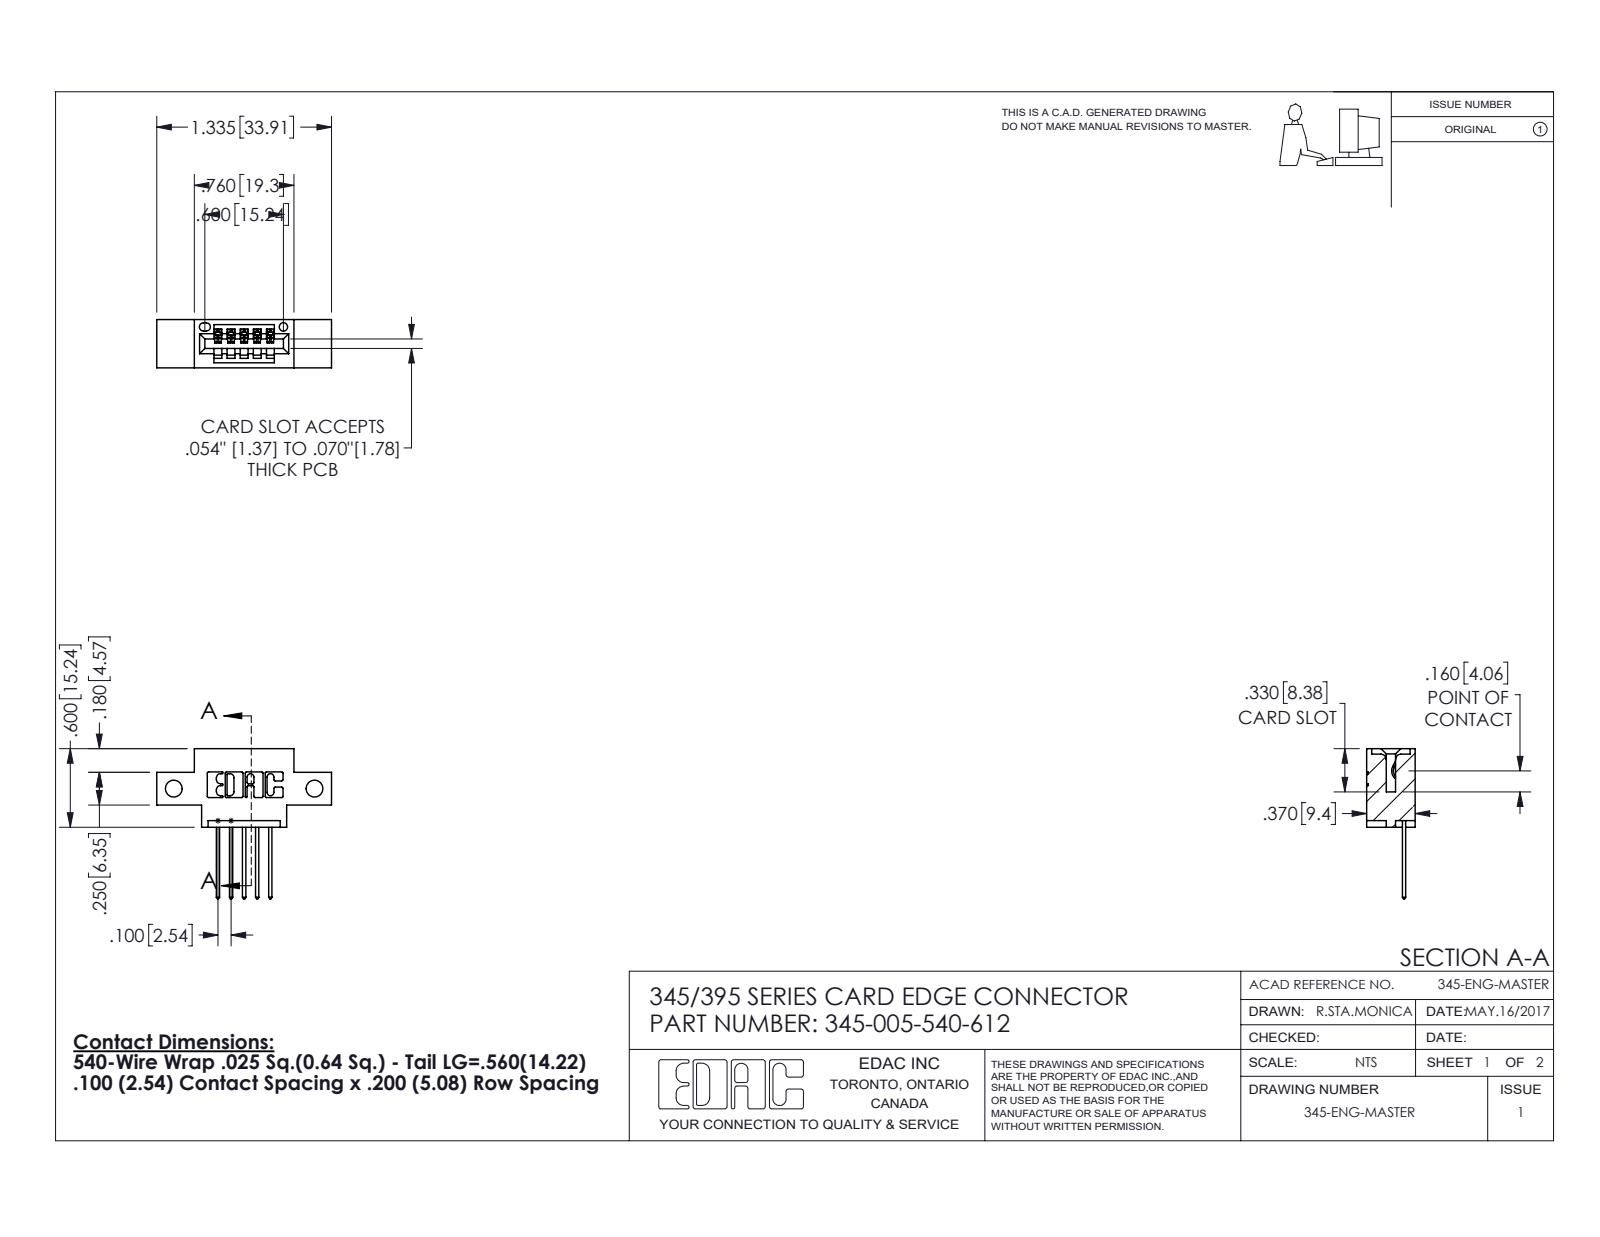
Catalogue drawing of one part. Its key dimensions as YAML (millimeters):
part_name: "345-005-540-612; 345 Part_0.170 Offset - Side Mount; 345-292-001_345-293-140"
step_written_by: "SolidWorks 2016 (CONFIG_CONTROL_DESIGN)"
units: millimeters
bodies: {solids: 6, faces: 420, planar: 284, cylindrical: 136, other: 0}
overall_size: [33.9, 29.1, 9.4]
volume: 2720
surface_area: 3150
round_holes:
  - {diameter: 3.3, count: 2}
  - {diameter: 1.6, count: 1}
partial_cylinders:
  - {radius: 0.3, count: 22}
  - {radius: 0.2, count: 10}
  - {radius: 0.3, count: 10}
  - {radius: 0.2, count: 6}
  - {radius: 0.8, count: 6}
  - {radius: 0.7, count: 3}
  - {radius: 0.8, count: 2}
  - {radius: 1, count: 2}
face_to_face_distances: [9.4, 5.1, 7.6, 1.8, 2.5, 0.6, 6.4, 2.5, 6.9, 1.5]
hole_center_spacings: [27.3]
